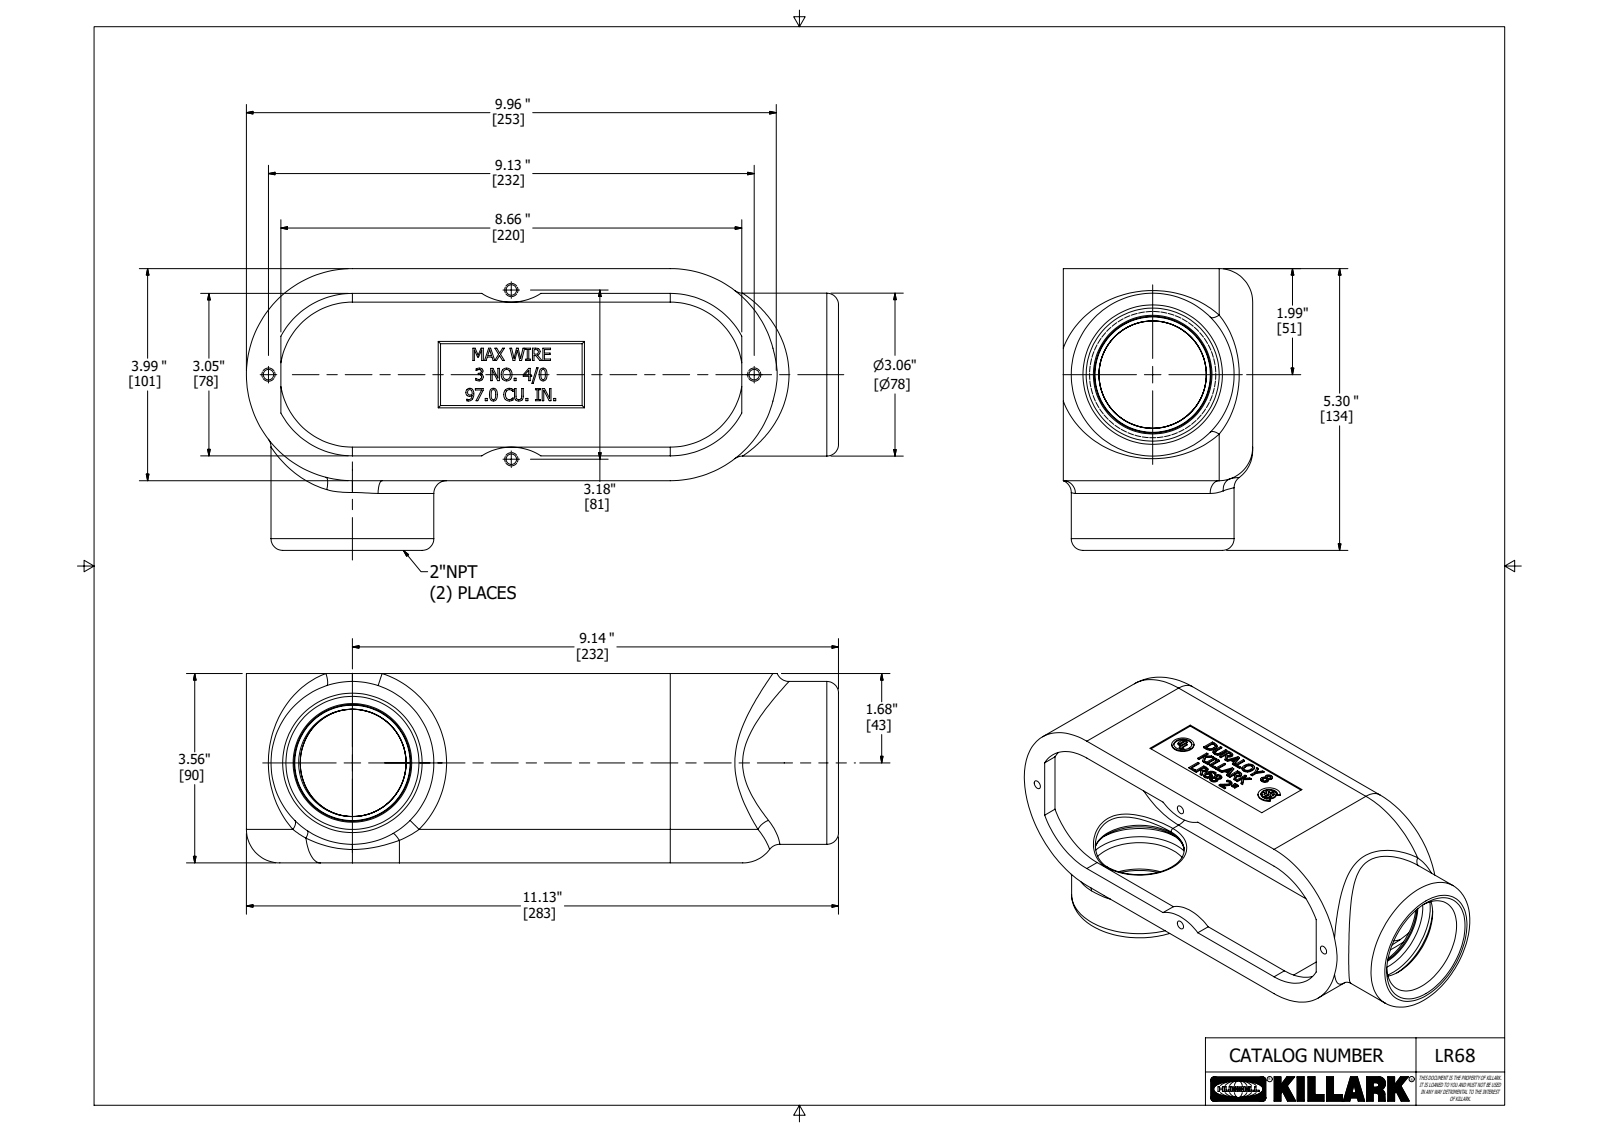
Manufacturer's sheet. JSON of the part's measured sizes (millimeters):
{"part_name": "21737-2", "step_written_by": "Autodesk Inventor 2018 (AUTOMOTIVE_DESIGN)", "units": "millimeters", "bodies": {"solids": 1, "faces": 762, "planar": 455, "cylindrical": 41, "other": 266}, "overall_size": [282.7, 134.5, 90.4], "volume_mm3": 525400, "surface_area_mm2": 177300, "round_holes": [[5, 4], [60.5, 2], [10.3, 1]], "round_bosses_or_shafts": [[77.7, 2], [12.7, 1]], "partial_cylinders_radius": [[10.9, 2], [16, 2], [26, 2], [38.8, 2], [45.5, 2], [50.6, 2], [0.4, 1], [1.6, 1]], "face_to_face_distances": [5.1, 96.1, 91.1, 101.2, 90.4, 85.3, 82, 77, 8.4, 0.8], "hole_center_spacings": [122.8, 41.3, 80.8, 231.9]}
